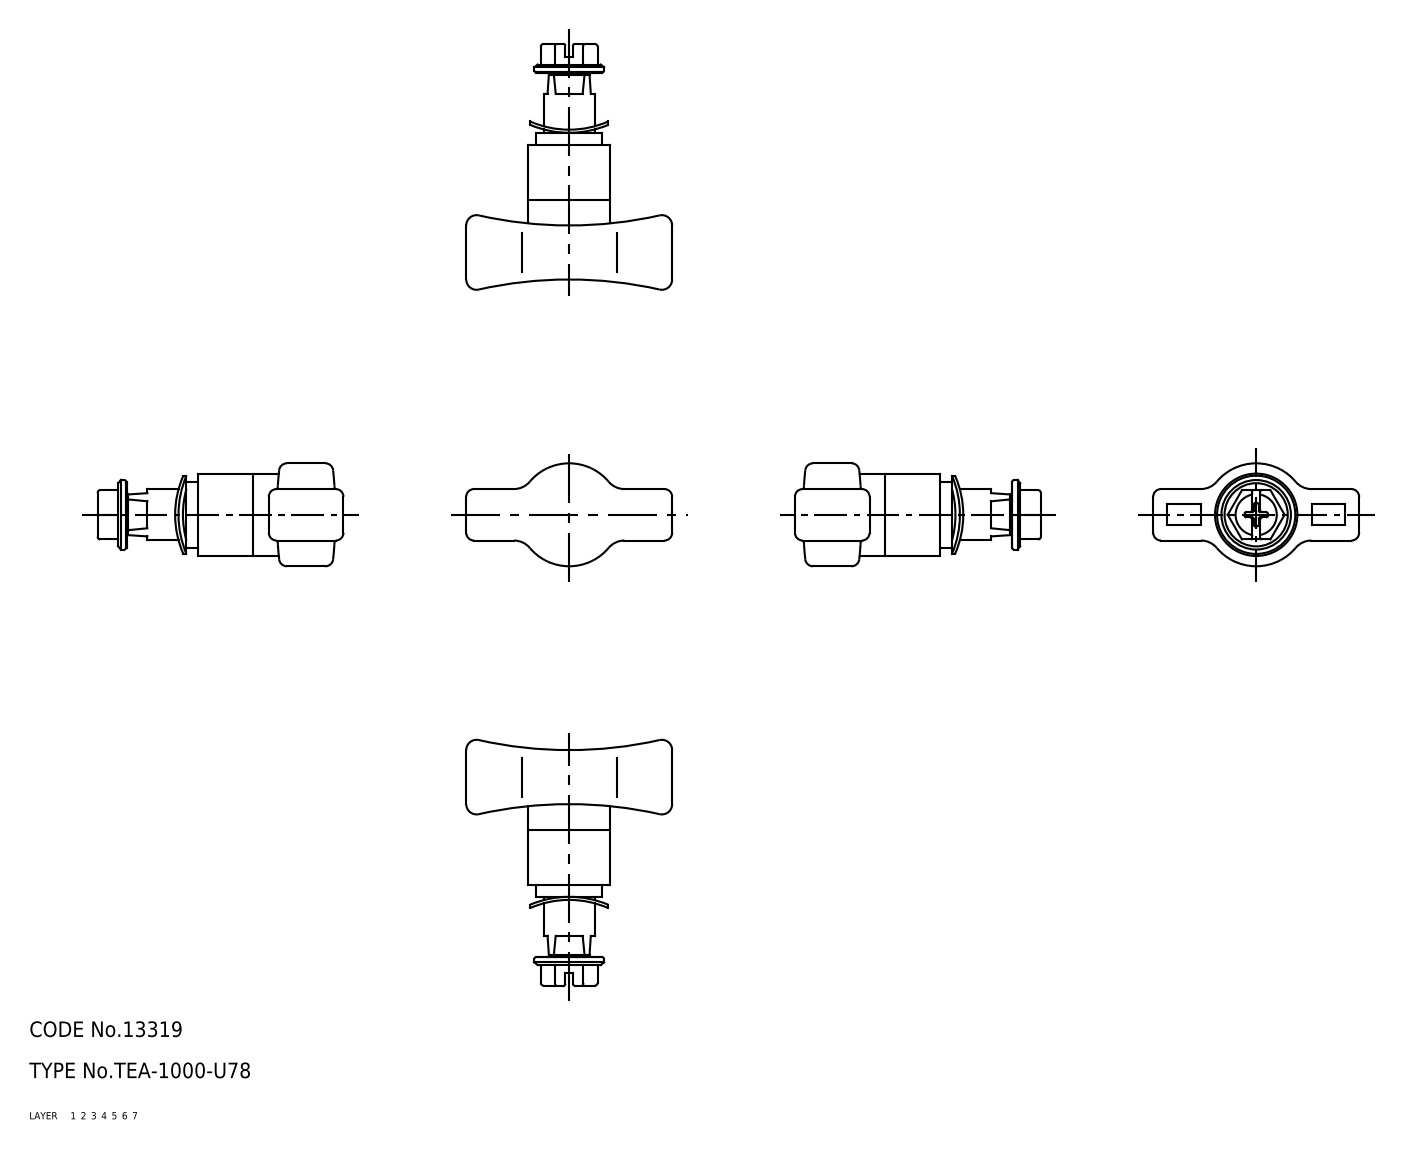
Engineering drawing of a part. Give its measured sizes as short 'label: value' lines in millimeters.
name: knob
written by: CADfix (AUTOMOTIVE_DESIGN)
unit: mm
bodies: 1 solid, 190 faces (0 planar, 0 cylindrical, 190 other)
size: 47.75 × 40 × 20
volume: 10 358 mm³; area: 4 346 mm²
